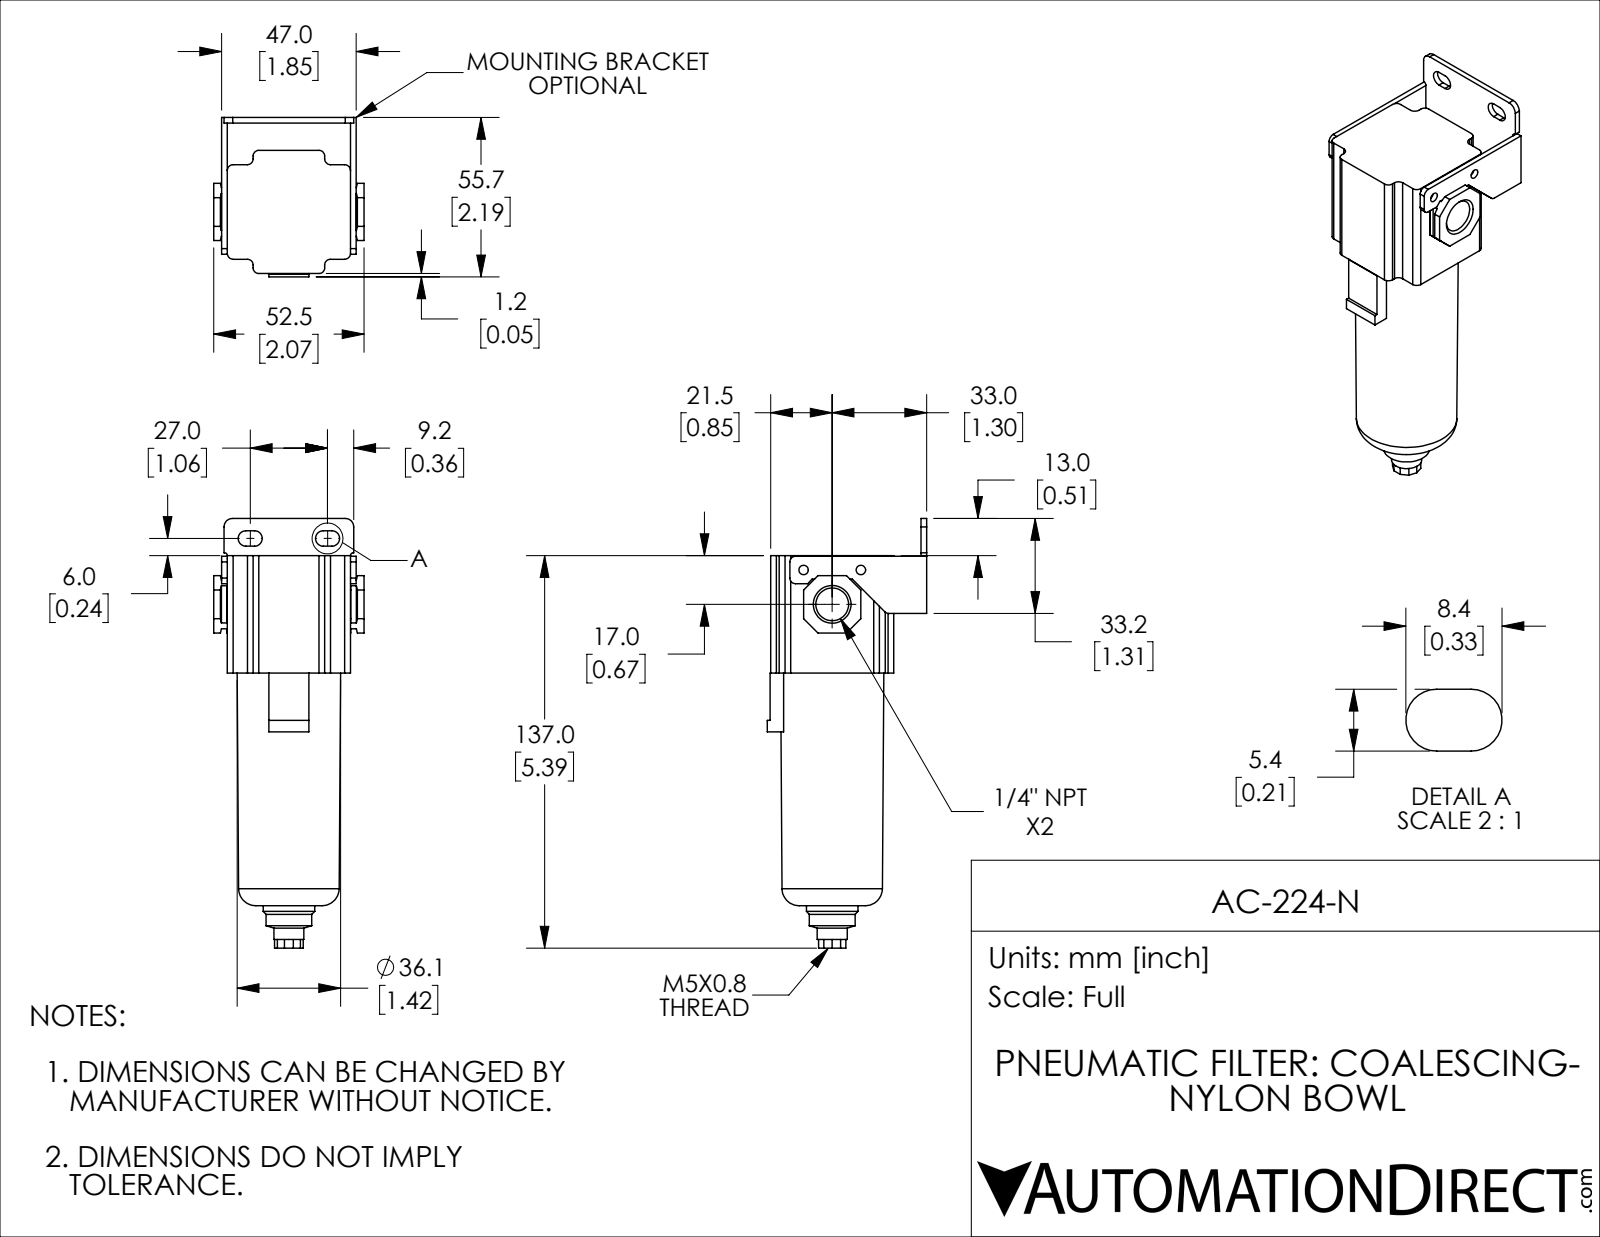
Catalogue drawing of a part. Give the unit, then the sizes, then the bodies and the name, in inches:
Units: inches
Overall size (bounding box): 5.906 × 2.192 × 2.067
Round holes (diameter × count): ⌀0.13 ×2, ⌀0.163 ×1, ⌀0.451 ×1
Round bosses / shafts (diameter × count): ⌀0.709 ×1, ⌀0.63 ×1, ⌀0.413 ×1
Partial cylindrical surfaces — rounded edges, fillets, slot ends (radius × count): R0.079 ×15, R0.106 ×4, R0.039 ×2, R0.118 ×2
Main face-to-face distances: 0.079, 1.693, 1.772, 2.067, 0.453, 2.146, 0.374, 0.197, 1.496, 1.614
Hole centre spacings: 0.615, 0.787
Volume: 9.618 in³ · Surface area: 40.63 in²
Bodies: 1 solid, 187 faces (125 planar, 48 cylindrical, 14 other)
Part name (STEP PRODUCT): AC-224-N
STEP written by: SolidWorks 2018 (AUTOMOTIVE_DESIGN)
